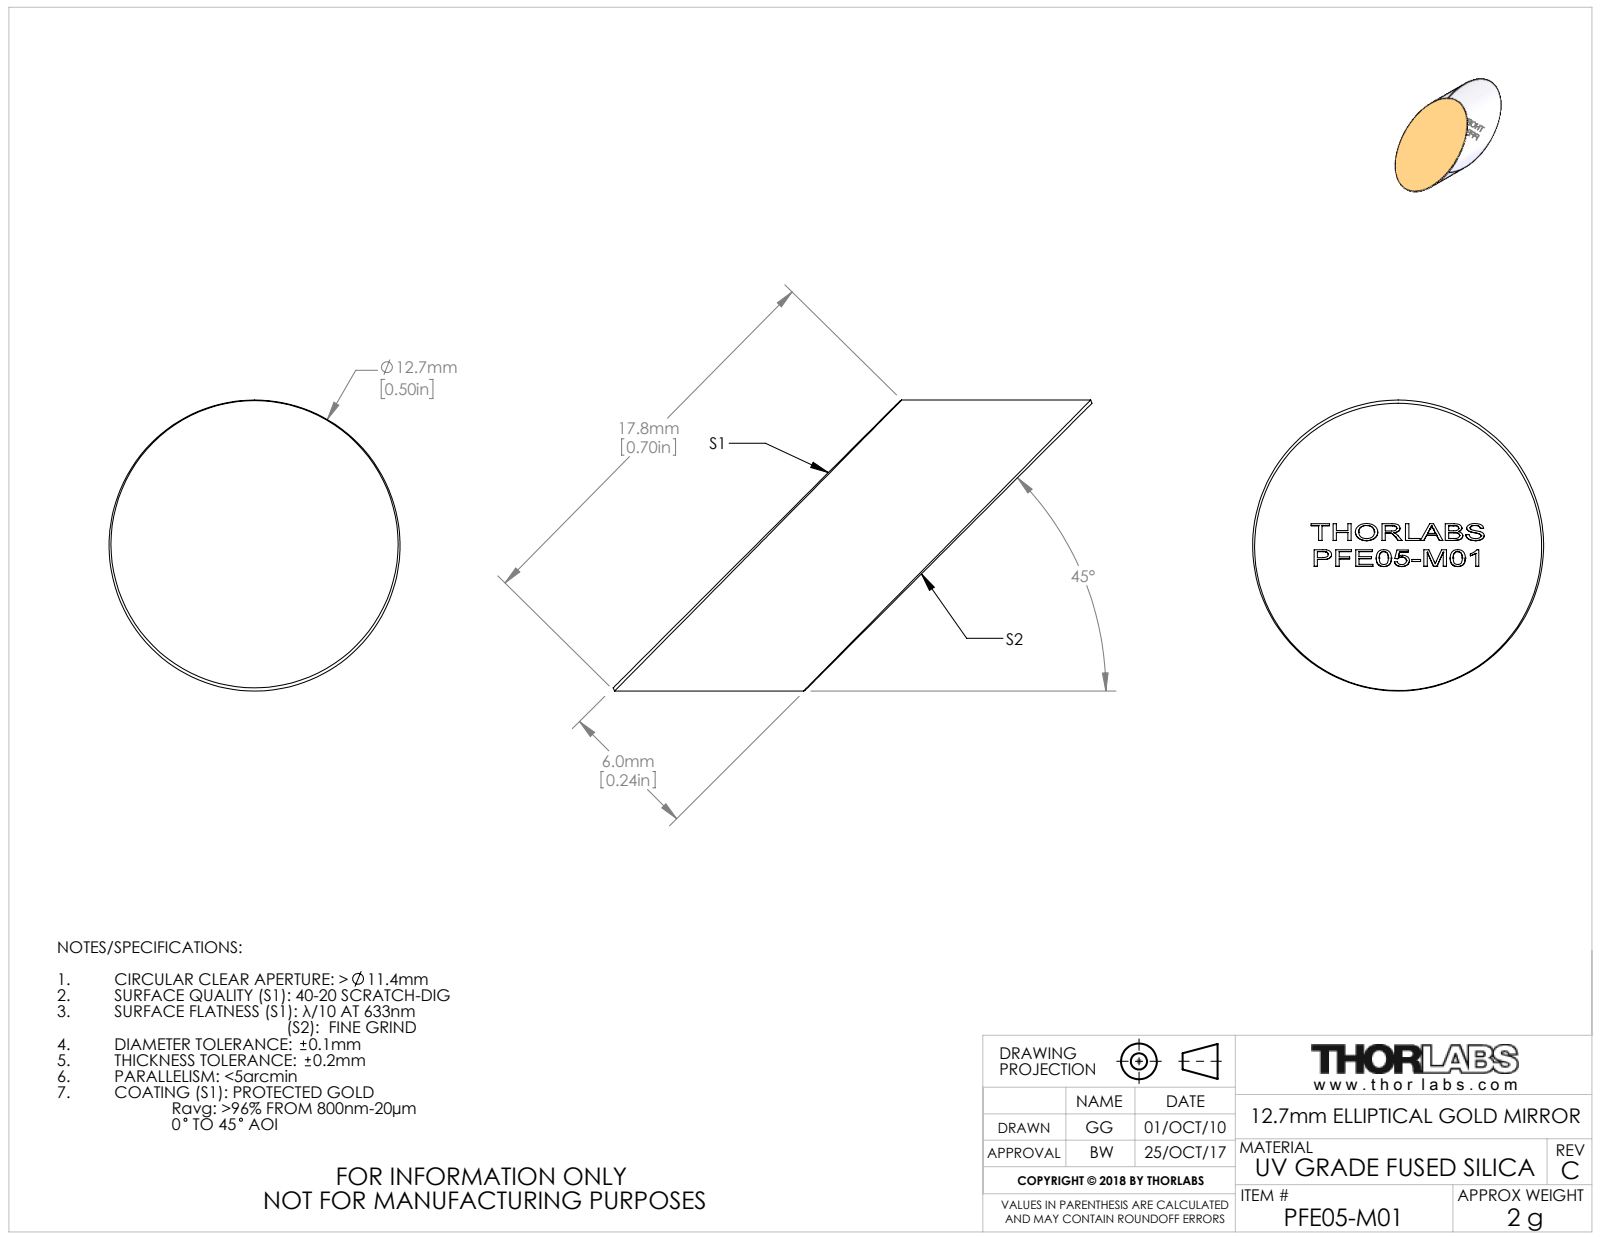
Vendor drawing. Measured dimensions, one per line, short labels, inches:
name: 21551-E0W
written by: SolidWorks 2016 (CONFIG_CONTROL_DESIGN)
unit: in
bodies: 1 solid, 232 faces (145 planar, 2 cylindrical, 85 other)
size: 0.823 × 0.5 × 0.5
volume: 0.066 in³; area: 1.068 in²
bosses: 1× ⌀0.5
face distances: 0.236, 0.063, 0.041, 0.036, 0.058, 0.064, 0.031, 0.033, 0.157, 0.099
